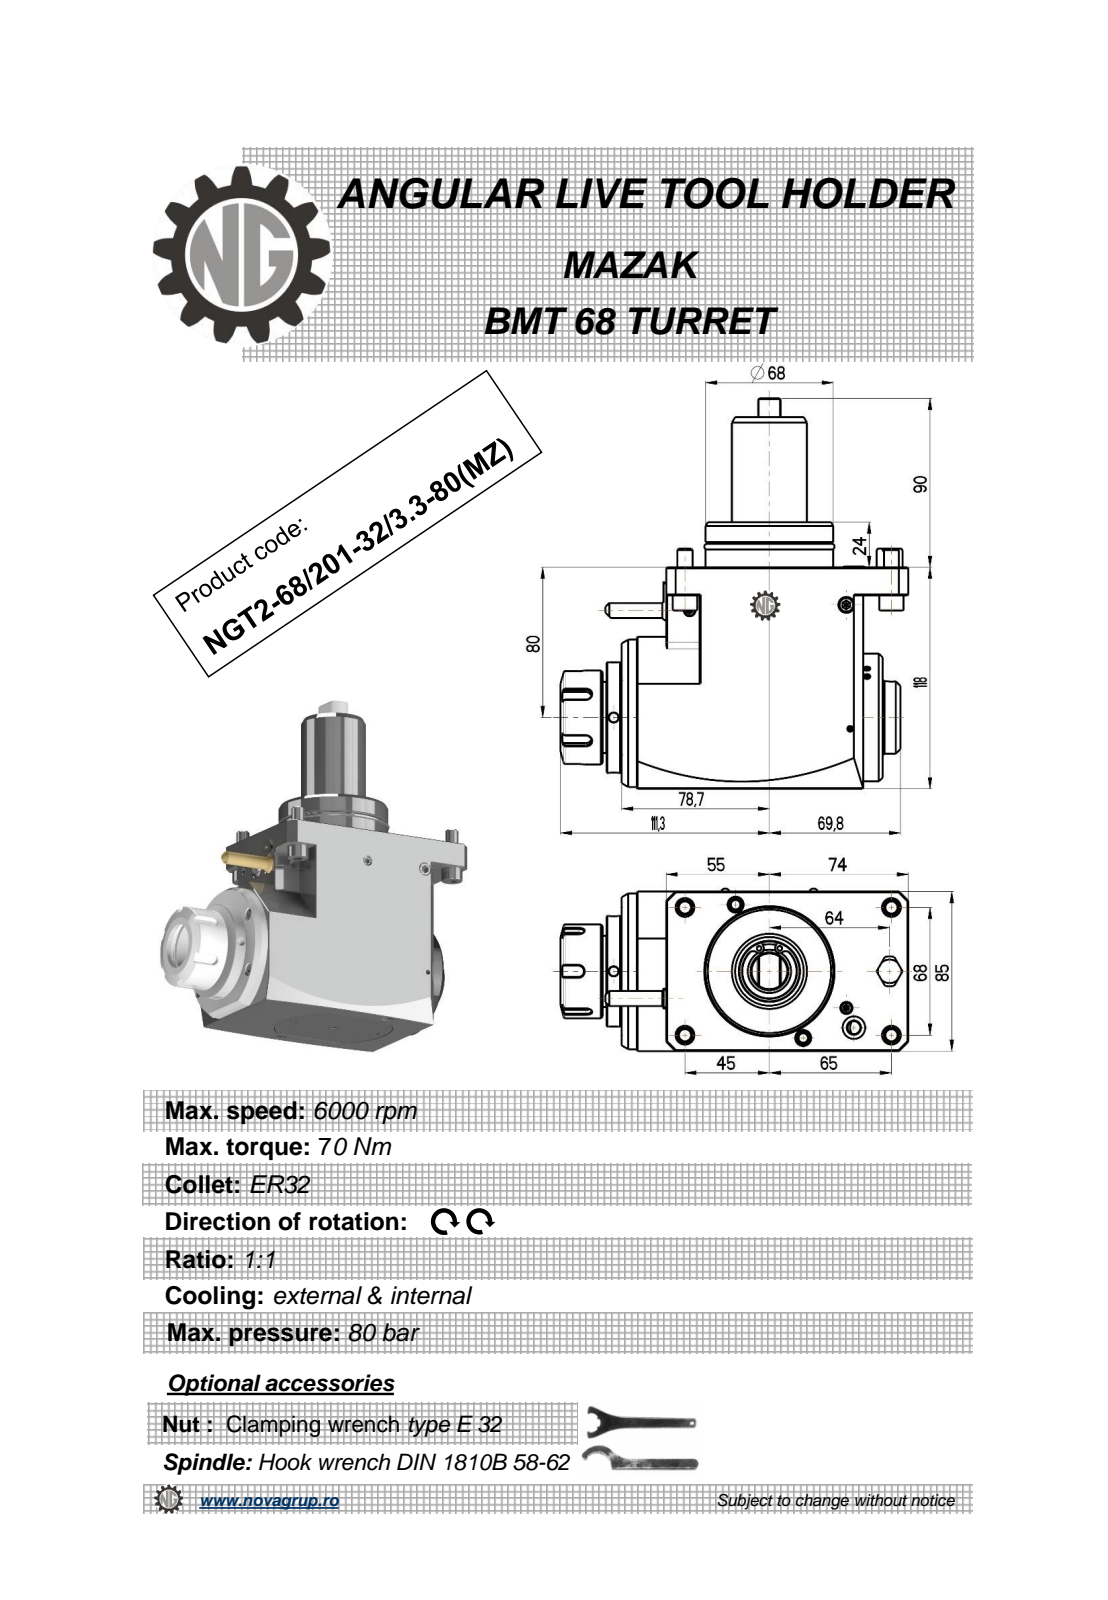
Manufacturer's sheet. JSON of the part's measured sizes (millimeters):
{"part_name": "NGT2_68_201_32_3_3_80_MZ", "step_written_by": "PRO/ENGINEER BY PARAMETRIC TECHNOLOGY CORPORATION, 2010280 (CONFIG_CONTROL_DESIGN)", "units": "millimeters", "bodies": {"solids": 2, "faces": 336, "planar": 140, "cylindrical": 85, "other": 111}, "overall_size": [208, 185.3, 85], "volume_mm3": 1468000, "surface_area_mm2": 105736, "round_holes": [[5, 3], [3, 1], [6.8, 1], [27, 1]], "round_bosses_or_shafts": [[8, 5], [13, 4], [68, 2], [83, 1], [63, 1], [59, 1], [50, 1], [47.4, 1]], "partial_cylinders_radius": [[0.22, 6], [3, 5], [5, 4], [0.8, 2], [550, 2], [3.4, 1], [8, 1], [10, 1]], "face_to_face_distances": [85, 118, 24, 128.7, 8, 103, 105, 142, 39, 15], "hole_center_spacings": [58.82, 131.42]}
